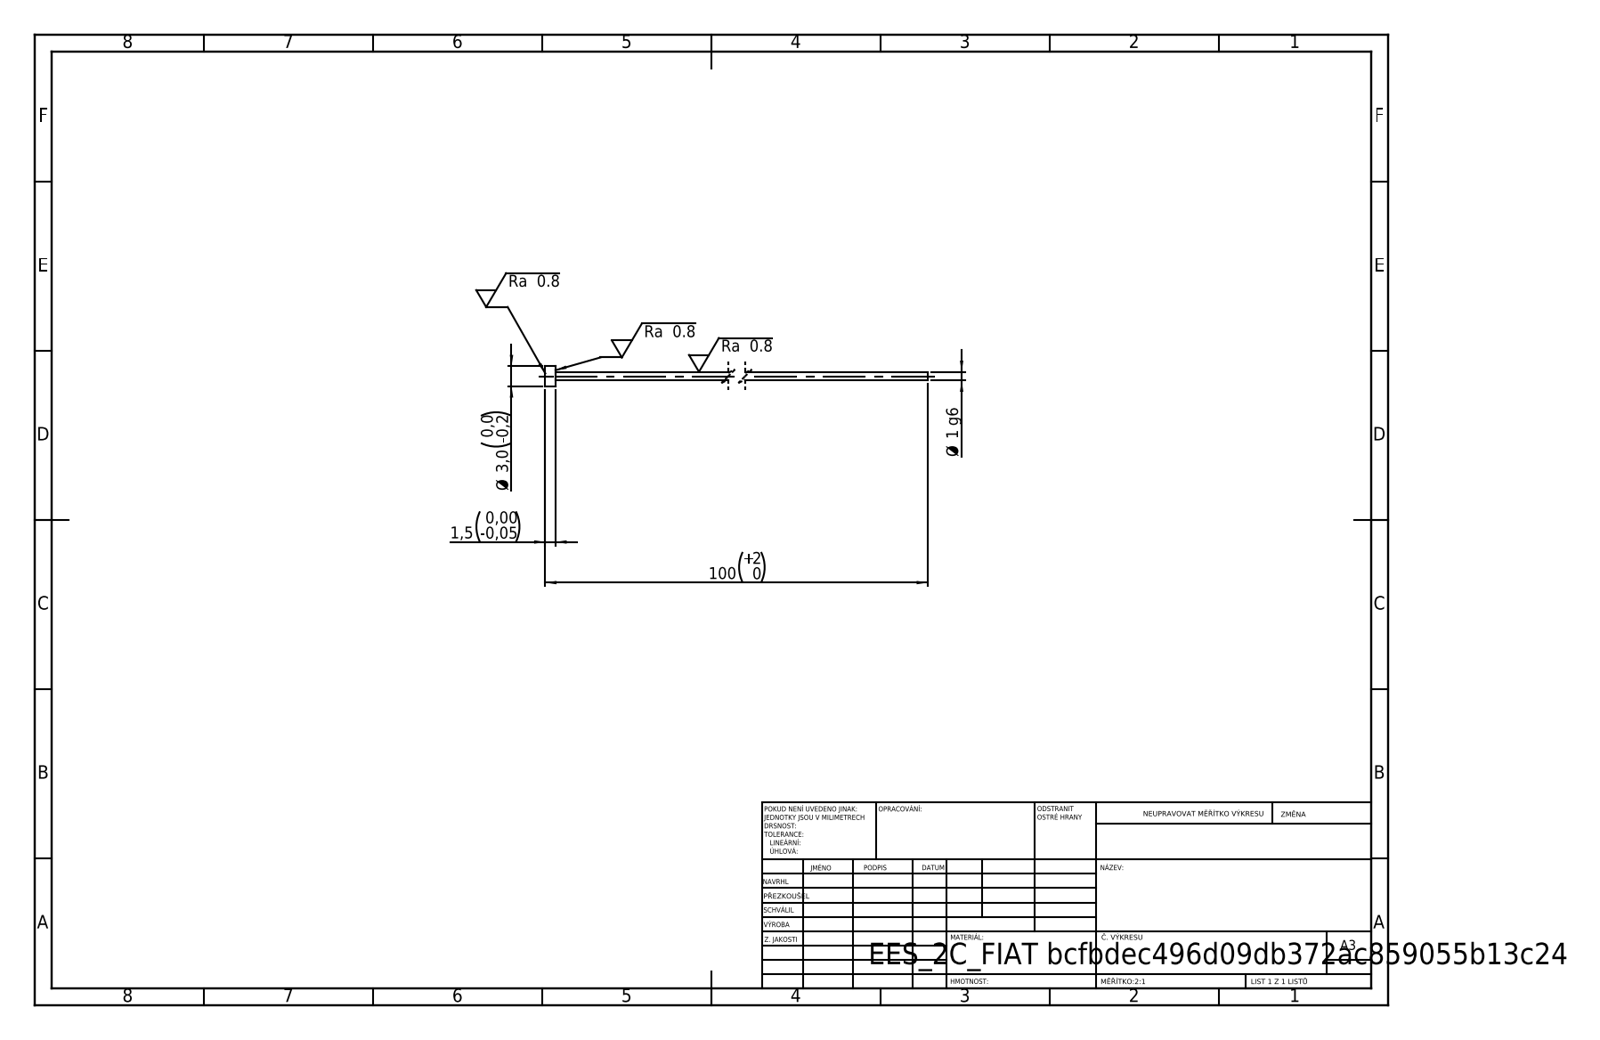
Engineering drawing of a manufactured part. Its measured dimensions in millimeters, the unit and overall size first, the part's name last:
Units: millimetres
Overall size (bounding box): 100 × 3 × 3
Round bosses / shafts (diameter × count): ⌀3 ×1, ⌀1.3 ×1
Main face-to-face distances: 1.5, 100, 98.5
Volume: 141 mm³ · Surface area: 431 mm²
Bodies: 1 solid, 7 faces (3 planar, 4 cylindrical, 0 other)
STEP written by: SolidWorks 2019 (CONFIG_CONTROL_DESIGN)
